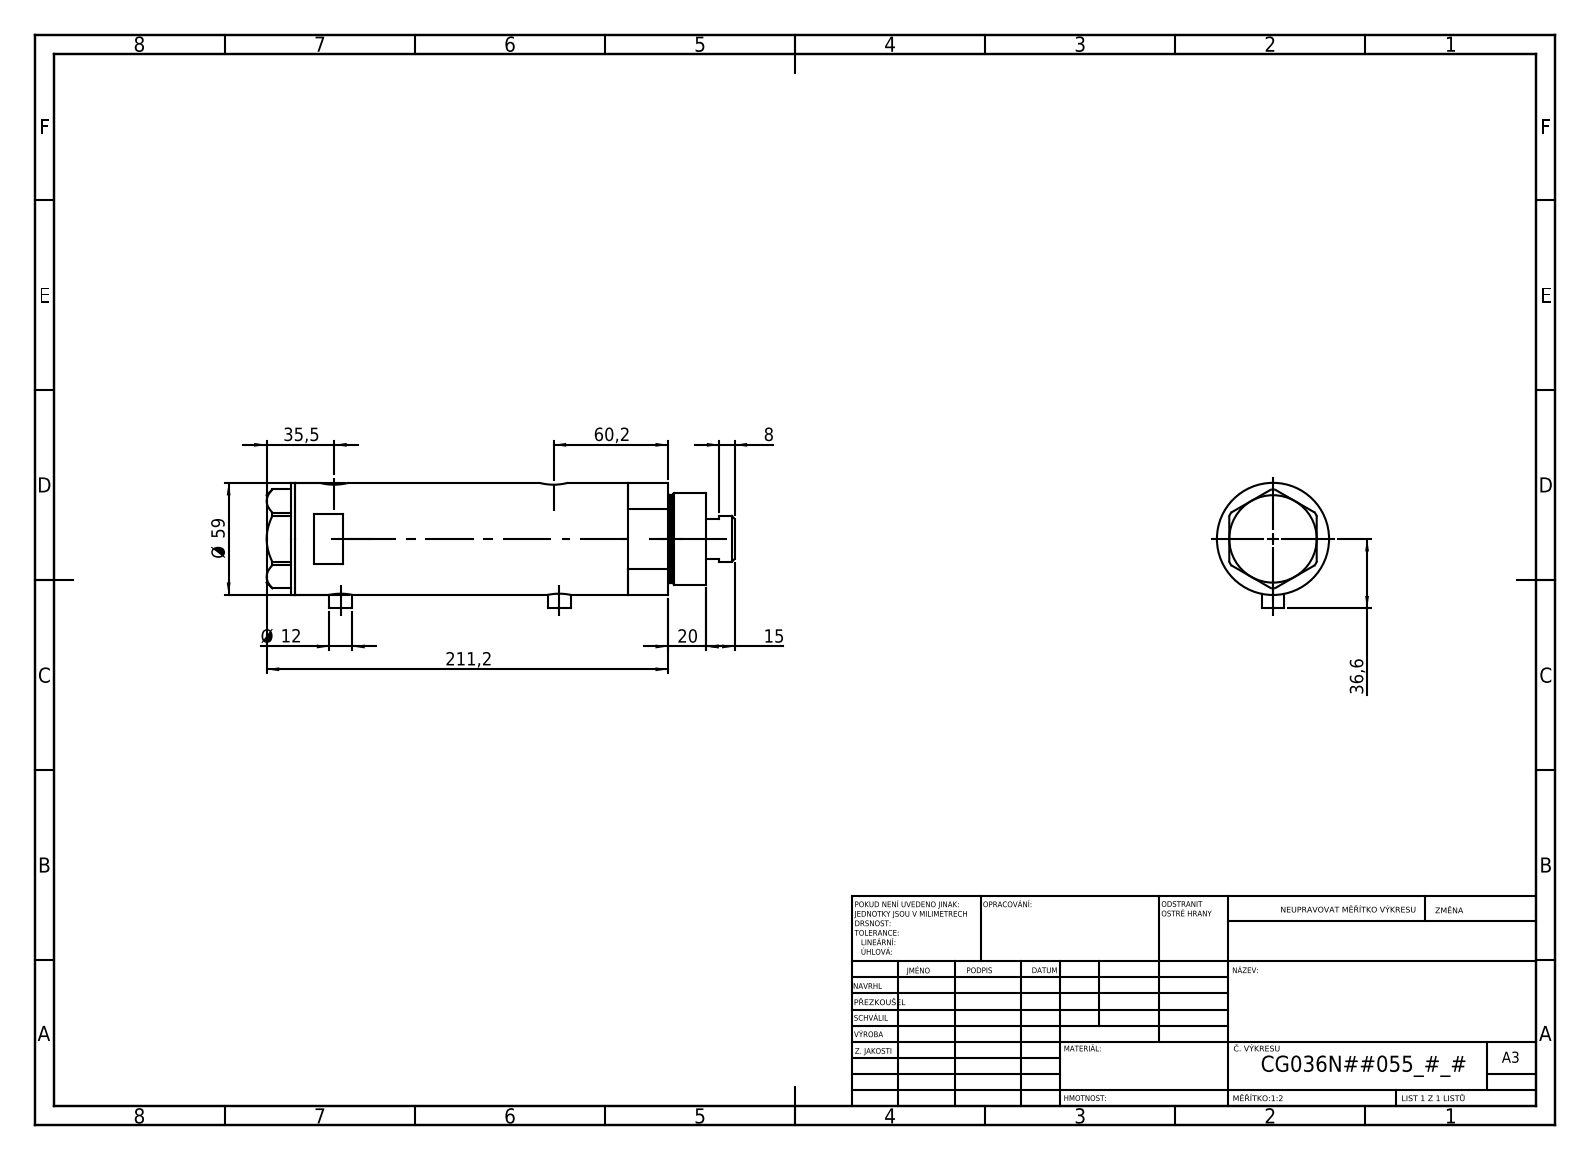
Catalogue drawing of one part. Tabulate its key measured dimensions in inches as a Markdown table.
| quantity | value |
| --- | --- |
| part name | V270CG_FRONT; V270CG_VC; V270CG_BACK; V270CG_MIDDLE |
| STEP written by | SolidWorks 2019 (CONFIG_CONTROL_DESIGN) |
| units | inches |
| bodies | 4 solids, 120 faces (51 planar, 49 cylindrical, 20 other) |
| overall size | 9.693 × 2.602 × 2.323 |
| volume | 34.87 in³ |
| surface area | 177 in² |
| round holes (diameter × count) | 0.383 × 2, 0.492 × 2, 0.591 × 2, 0.335 × 1, 0.984 × 1, 1.043 × 1, 1.417 × 1, 1.575 × 1, 2.047 × 1 |
| round bosses / shafts (diameter × count) | 0.472 × 2, 2.323 × 1, 1.89 × 1, 1.811 × 1, 0.945 × 1 |
| main face-to-face distances | 5.402, 0.925, 4.476, 0.591, 1.516, 5.992, 0.079, 9.102, 8.512, 7.587 |
| hole center spacings | 0.114, 0.138, 4.409, 4.524, 4.547, 4.661 |
